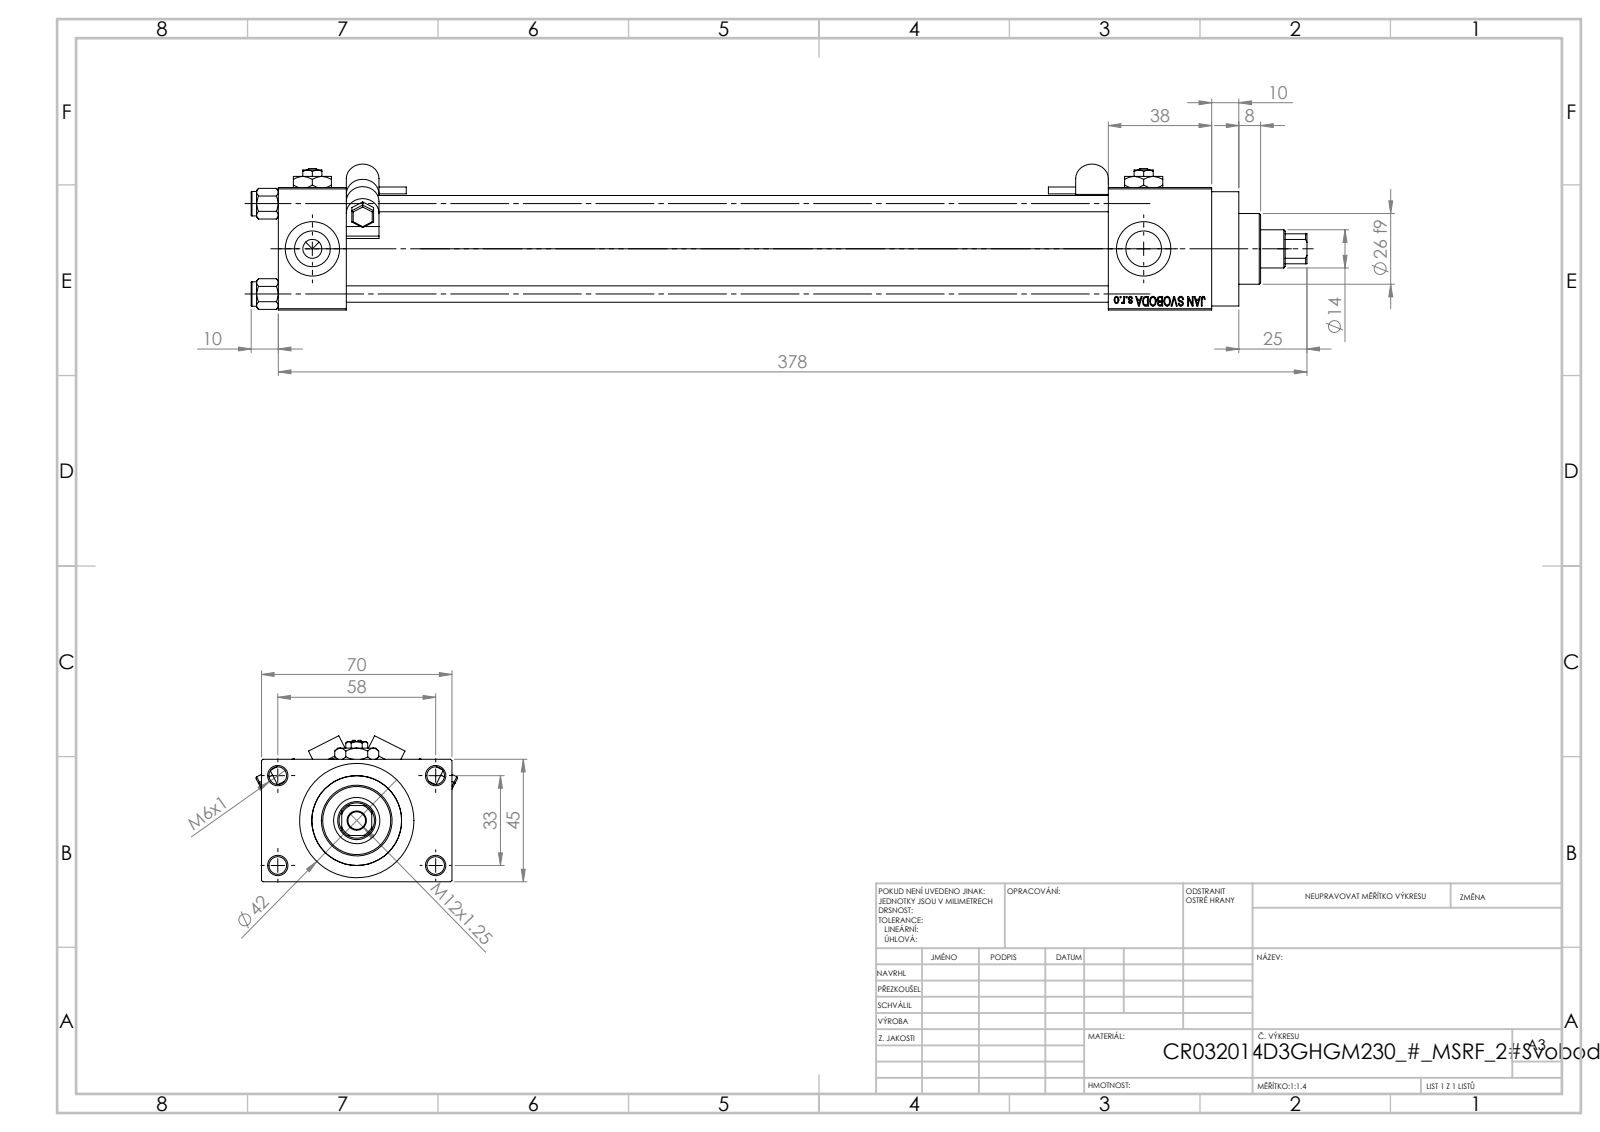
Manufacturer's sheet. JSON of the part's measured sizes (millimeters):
{"part_name": "MSRF_MSRG1; V215CR_D_TYCINKA; V215CR_D_Body; V215_VC_A (+3 more)", "step_written_by": "SolidWorks 2019 (CONFIG_CONTROL_DESIGN)", "units": "millimeters", "bodies": {"solids": 15, "faces": 1265, "planar": 578, "cylindrical": 127, "other": 560}, "overall_size": [388, 74.05, 53.66], "volume_mm3": 373317, "surface_area_mm2": 159363, "round_holes": [[6.5, 5], [6, 4], [13.16, 4], [20, 4], [7, 3], [14, 1], [17, 1], [24, 1], [32, 1], [33, 1]], "round_bosses_or_shafts": [[9, 4], [5, 2], [2.5, 2], [42, 1], [38, 1], [26, 1]], "partial_cylinders_radius": [[0.5, 12], [6, 4], [6.5, 1]], "face_to_face_distances": [45, 25, 280, 12.5, 305, 57.5, 318, 38, 343, 70], "hole_center_spacings": [12.4, 23.48, 33.2, 33.37, 35.35, 45.6, 56.35, 33]}
